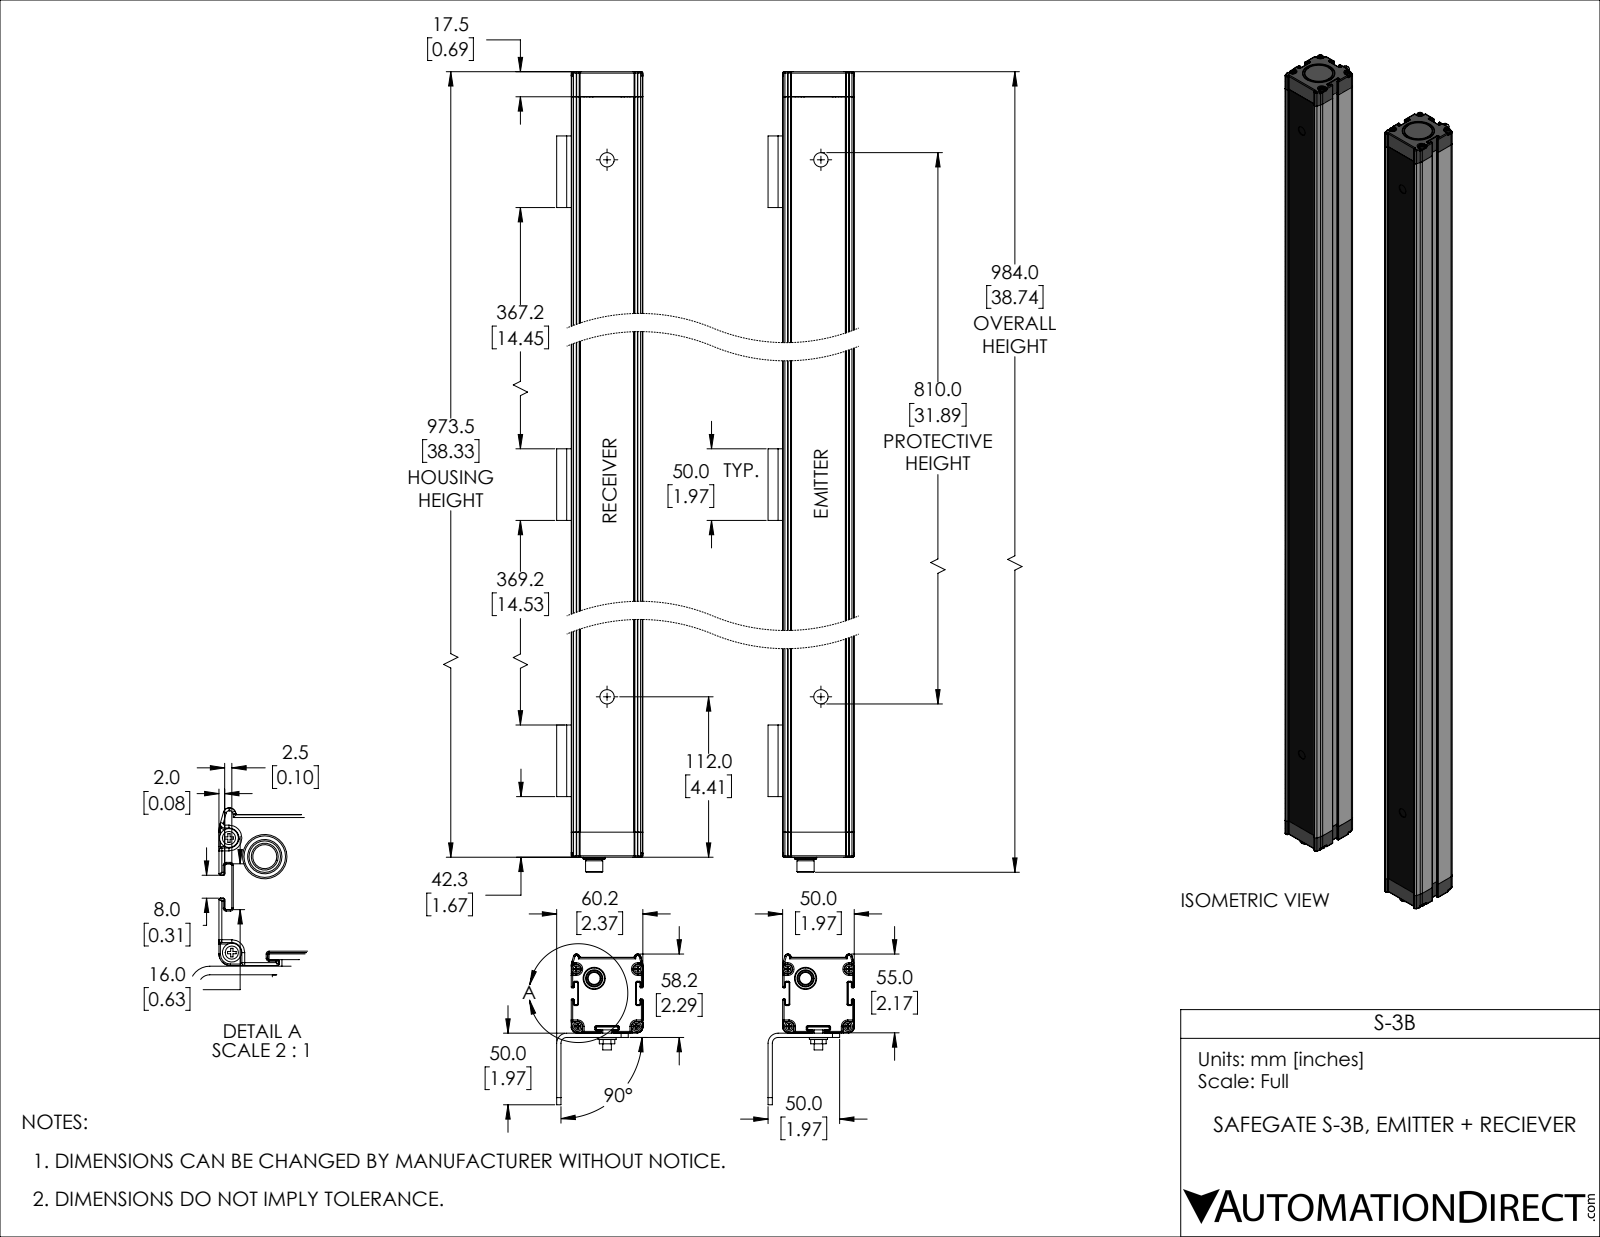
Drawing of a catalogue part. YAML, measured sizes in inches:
part_name: "S-3B; S-3B_1; S-3B_2"
step_written_by: "SolidWorks 2019 (AUTOMOTIVE_DESIGN)"
units: inches
bodies: {solids: 61, faces: 4254, planar: 1924, cylindrical: 1590, other: 740}
overall_size: [38.744, 8.082, 4.391]
volume: 101.6
surface_area: 1999
round_holes:
  - {diameter: 0.236, count: 12}
  - {diameter: 0.31, count: 11}
  - {diameter: 0.138, count: 8}
  - {diameter: 0.472, count: 6}
  - {diameter: 0.551, count: 6}
  - {diameter: 0.079, count: 4}
  - {diameter: 0.378, count: 2}
  - {diameter: 0.394, count: 2}
round_bosses_or_shafts:
  - {diameter: 0.177, count: 12}
  - {diameter: 0.5, count: 11}
  - {diameter: 0.591, count: 8}
  - {diameter: 0.26, count: 8}
  - {diameter: 0.61, count: 2}
  - {diameter: 0.472, count: 2}
  - {diameter: 0.433, count: 2}
partial_cylinders:
  - {radius: 0.02, count: 423}
  - {radius: 0.039, count: 208}
  - {radius: 0.012, count: 52}
  - {radius: 0.128, count: 48}
  - {radius: 0.197, count: 24}
  - {radius: 0.138, count: 16}
  - {radius: 0.059, count: 13}
  - {radius: 0.079, count: 10}
face_to_face_distances: [0.247, 0.098, 5.713, 0.177, 0.276, 1.693, 1.791, 0.079, 0.118, 1.969]
hole_center_spacings: [5.718, 0.406, 1.139, 1.181, 5.713, 5.833, 0.555, 0.626]
